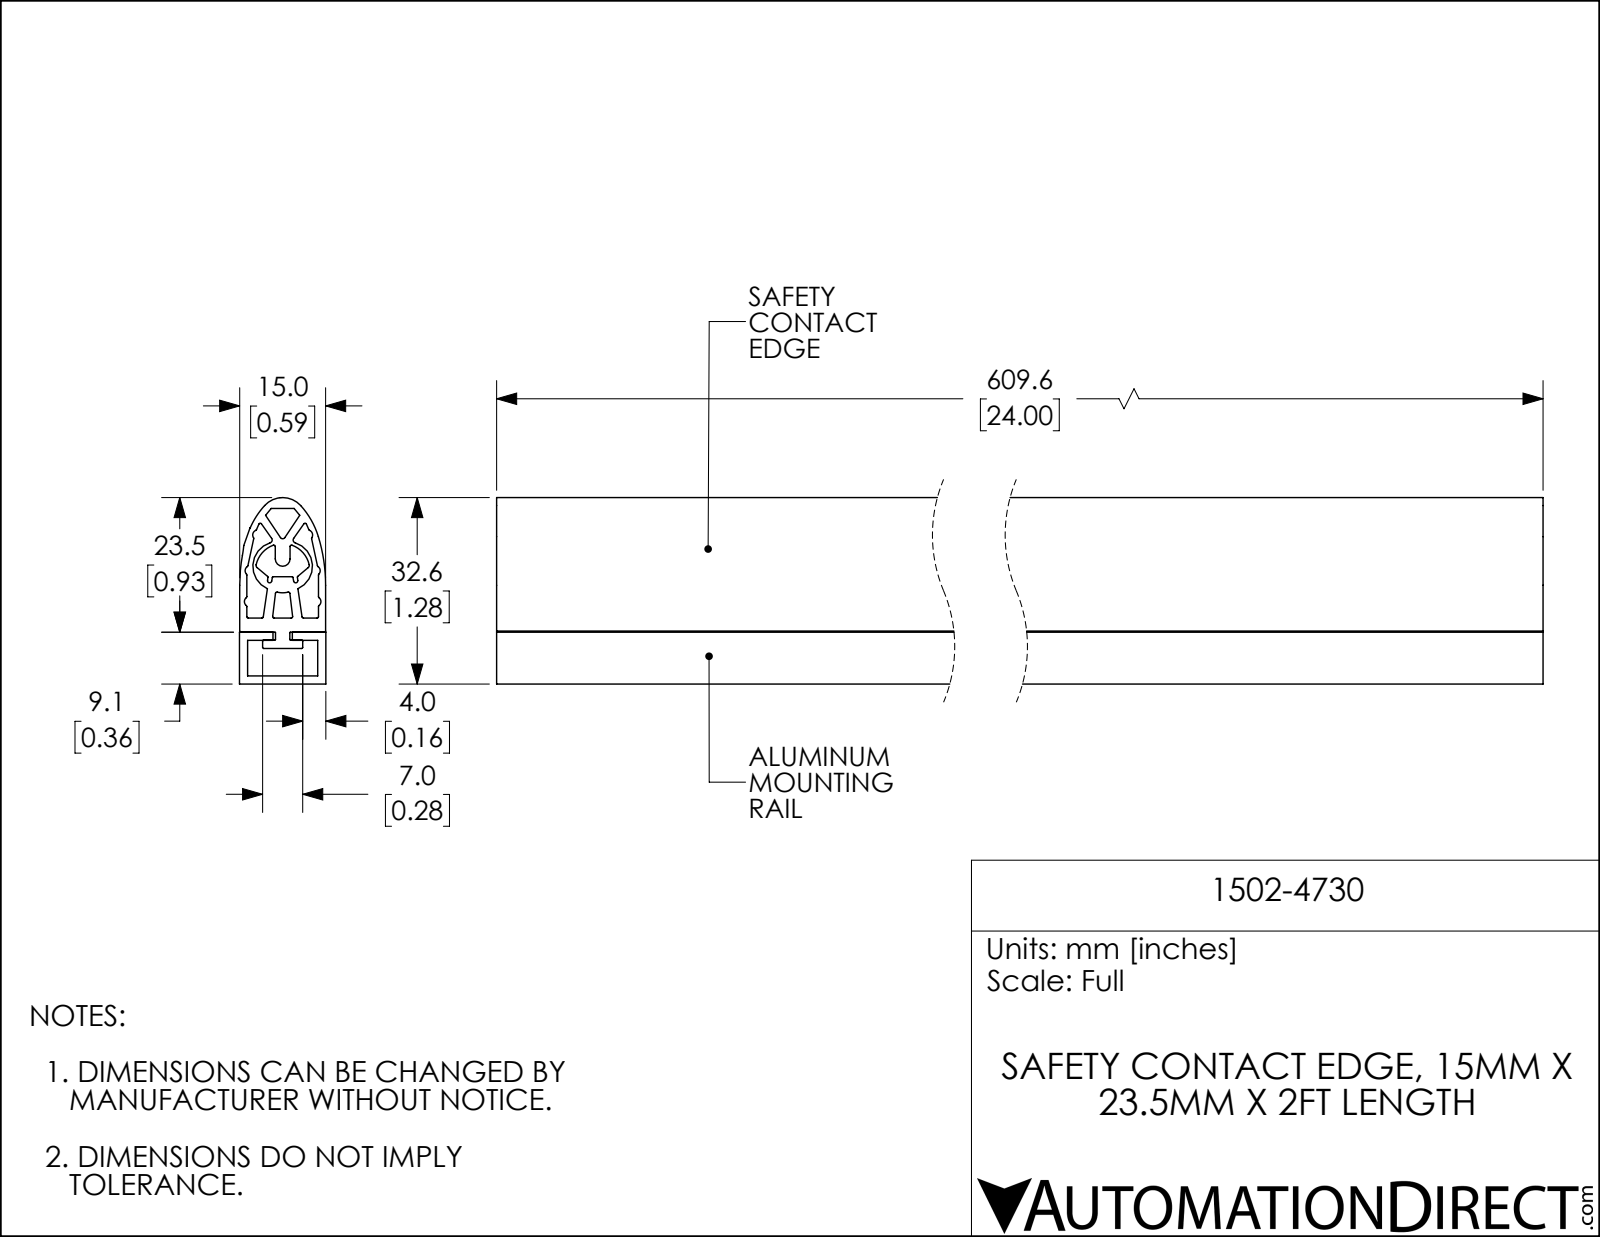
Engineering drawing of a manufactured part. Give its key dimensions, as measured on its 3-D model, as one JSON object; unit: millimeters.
{"part_name": "1502-4730", "step_written_by": "SolidWorks 2018 (AUTOMOTIVE_DESIGN)", "units": "millimeters", "bodies": {"solids": 2, "faces": 123, "planar": 59, "cylindrical": 57, "other": 7}, "overall_size": [609.6, 32.5, 15.1], "volume_mm3": 142100, "surface_area_mm2": 189200, "partial_cylinders_radius": [[0.3, 24], [0.9, 6], [0.1, 4], [0.2, 4], [0.5, 4], [0.4, 2], [4.3, 2], [14.3, 2]], "face_to_face_distances": [1.4, 7.6, 6.2, 15, 9, 13.7, 1.4, 13.6, 15.1, 4.8]}
